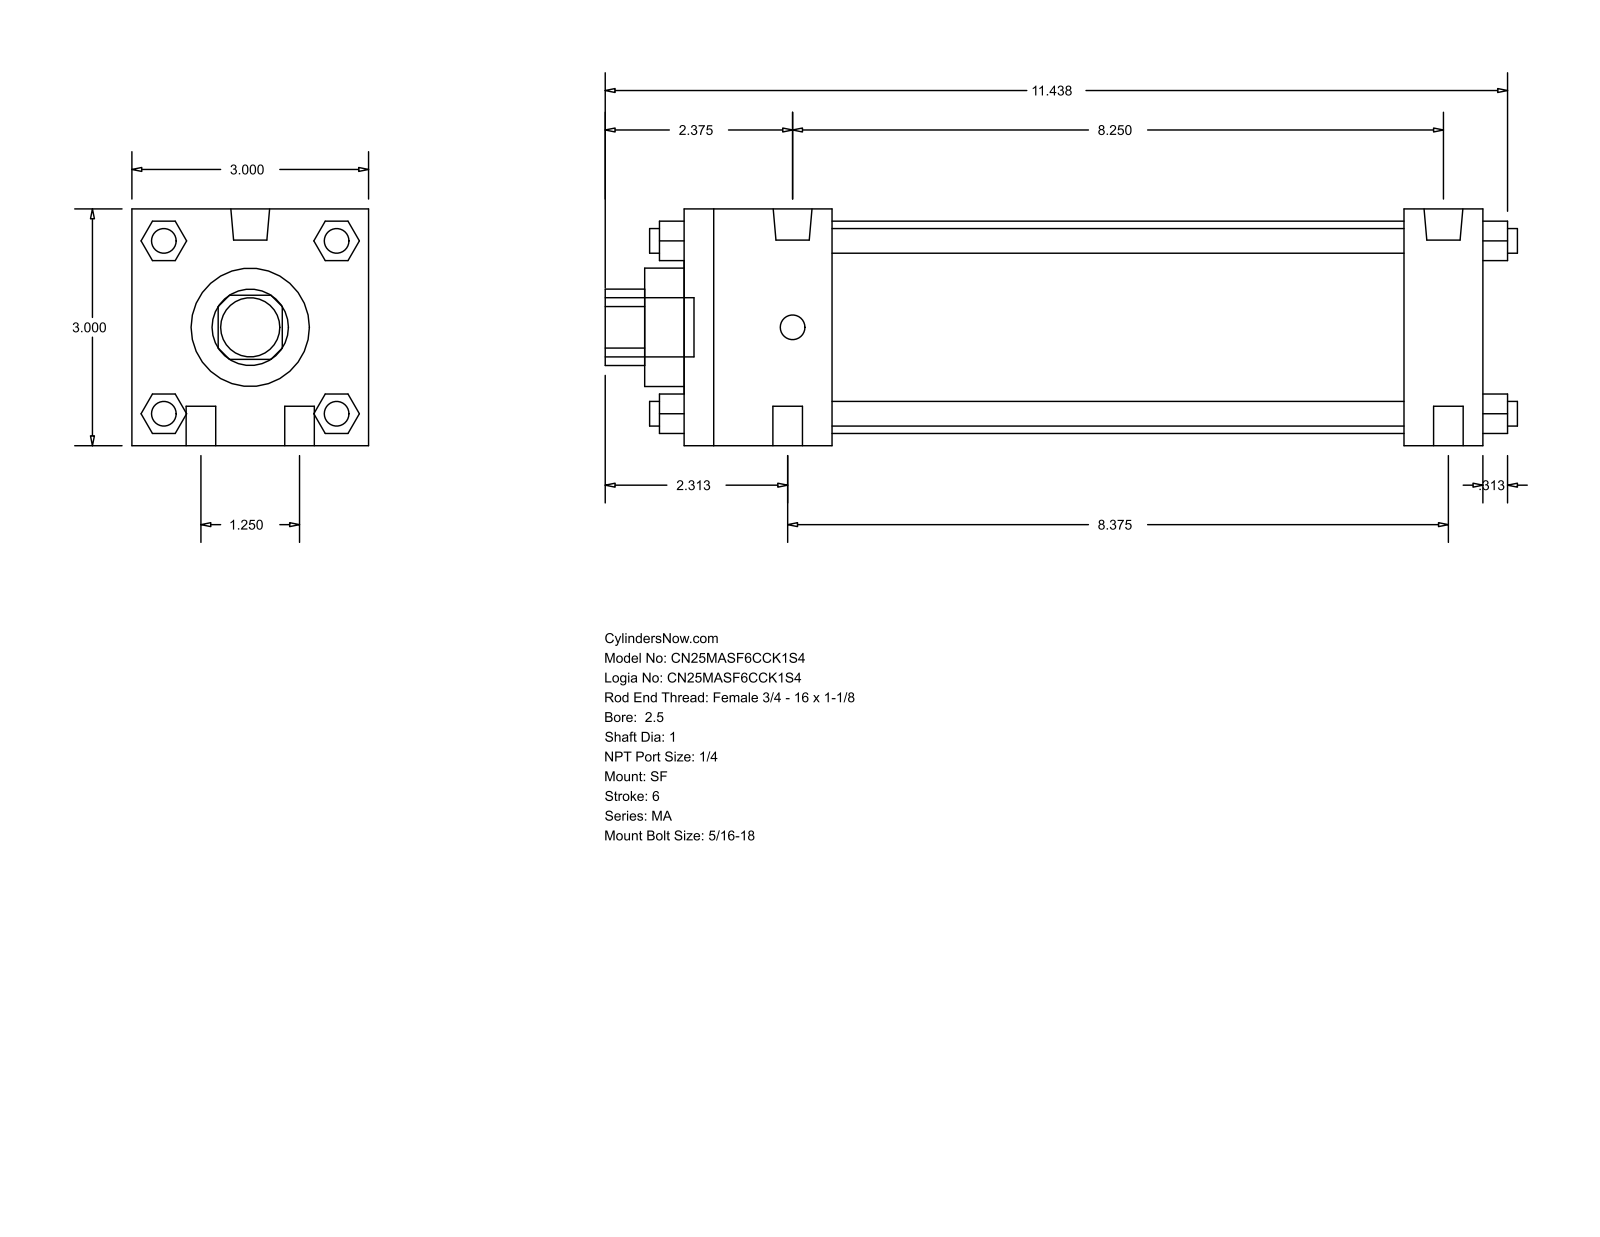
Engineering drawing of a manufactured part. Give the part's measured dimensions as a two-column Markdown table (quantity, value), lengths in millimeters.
| quantity | value |
| --- | --- |
| part name | MA_SF__0250_1 |
| STEP written by | GSSL Pune (CONFIG_CONTROL_DESIGN) |
| units | millimeters |
| bodies | 0 solids, 124 faces (94 planar, 30 cylindrical, 0 other) |
| overall size | 293.69 × 76.2 × 76.2 |
| round holes (diameter × count) | 25.4 × 1, 38.1 × 1, 68.33 × 1 |
| round bosses / shafts (diameter × count) | 7.94 × 6, 9.53 × 4, 12.49 × 2, 19.05 × 1 |
| partial cylindrical surfaces (radius × count) | 12.29 × 1 |
| main face-to-face distances | 76.2, 257.17, 12.7, 231.78, 25.39, 47.63, 184.15, 209.54, 27.81, 48.17 |
